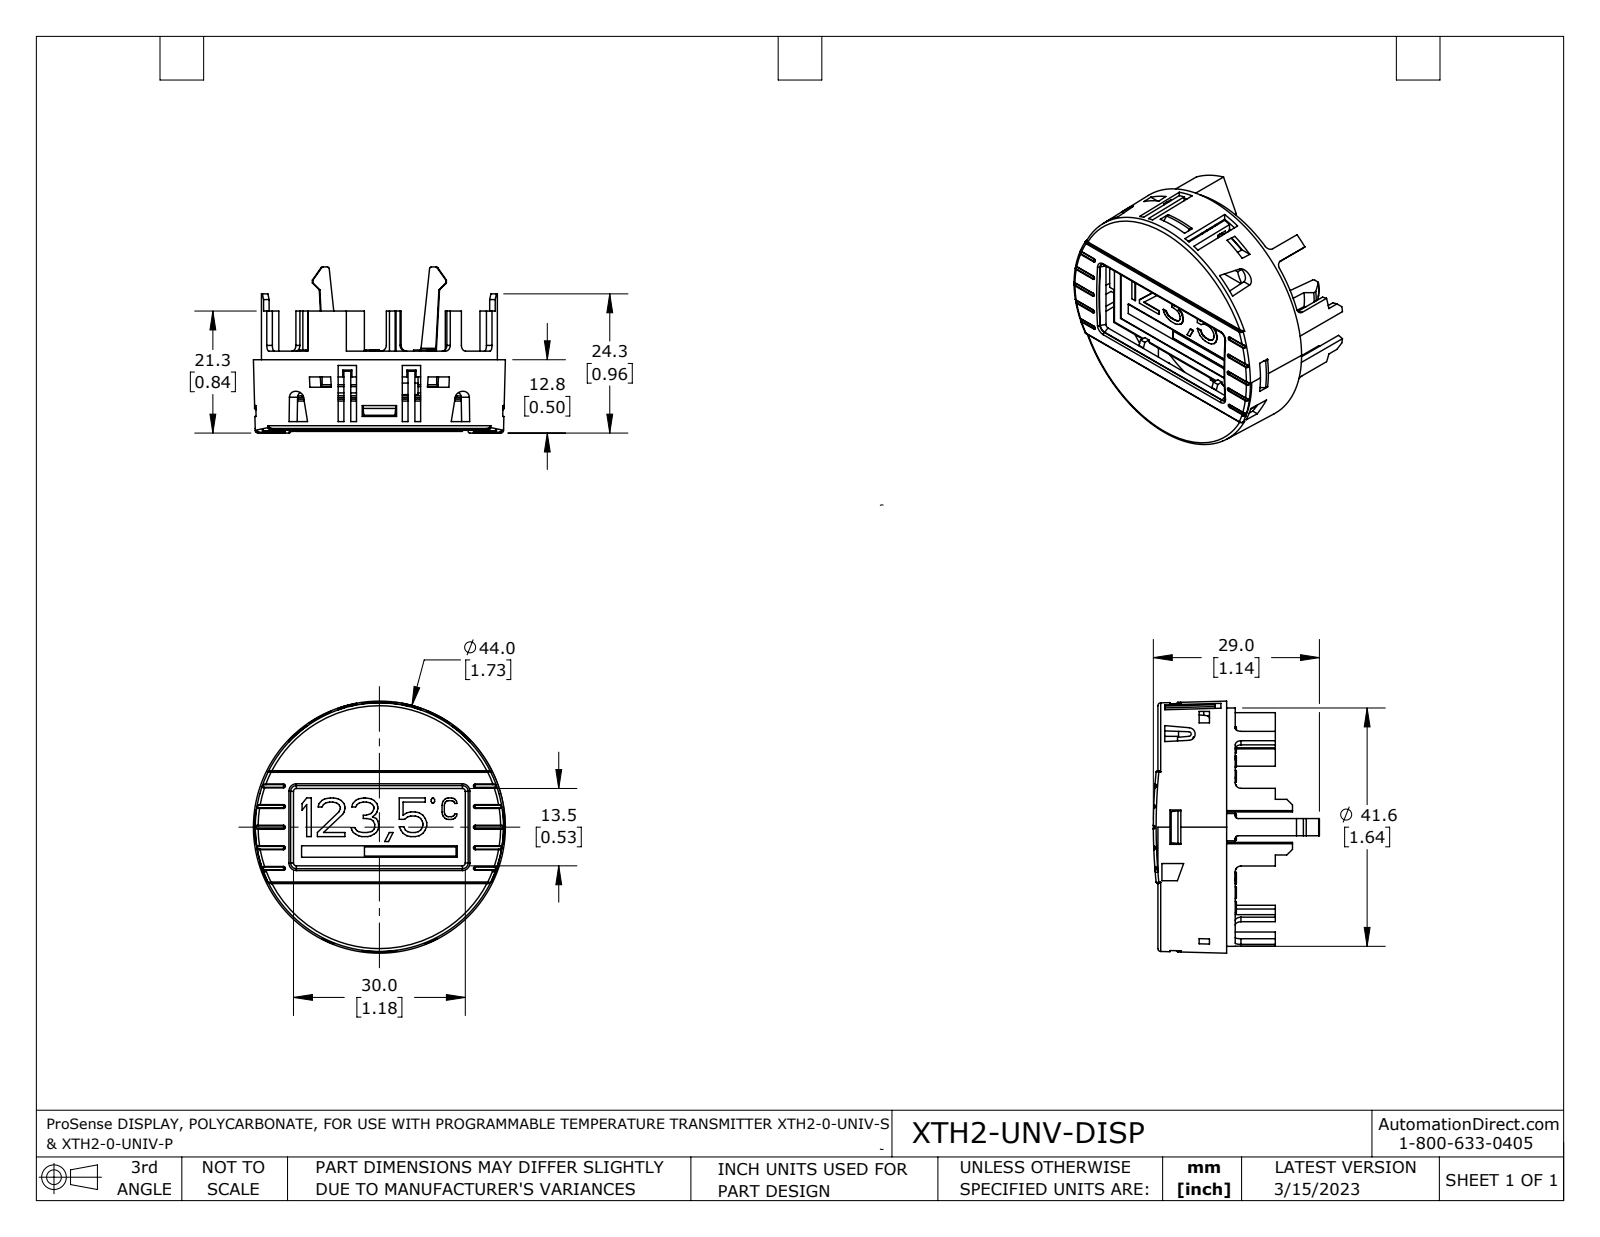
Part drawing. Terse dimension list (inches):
name: XTH2-UNV-DISP
written by: SolidWorks 2021 (AUTOMOTIVE_DESIGN)
unit: in
bodies: 1 solid, 2024 faces (1803 planar, 116 cylindrical, 105 other)
size: 1.732 × 1.732 × 1.142
volume: 0.484 in³; area: 20.72 in²
holes: 1× ⌀1.52
bosses: 1× ⌀1.638
rounds: 22× R0.039, 12× R0.004, 5× R0.01, 3× R0.02, 2× R0.008, 2× R0.012, 2× R0.047, 2× R0.059
face distances: 0.059, 0.425, 0.047, 0.531, 0.472, 0.484, 0.172, 0.254, 0.231, 0.301
